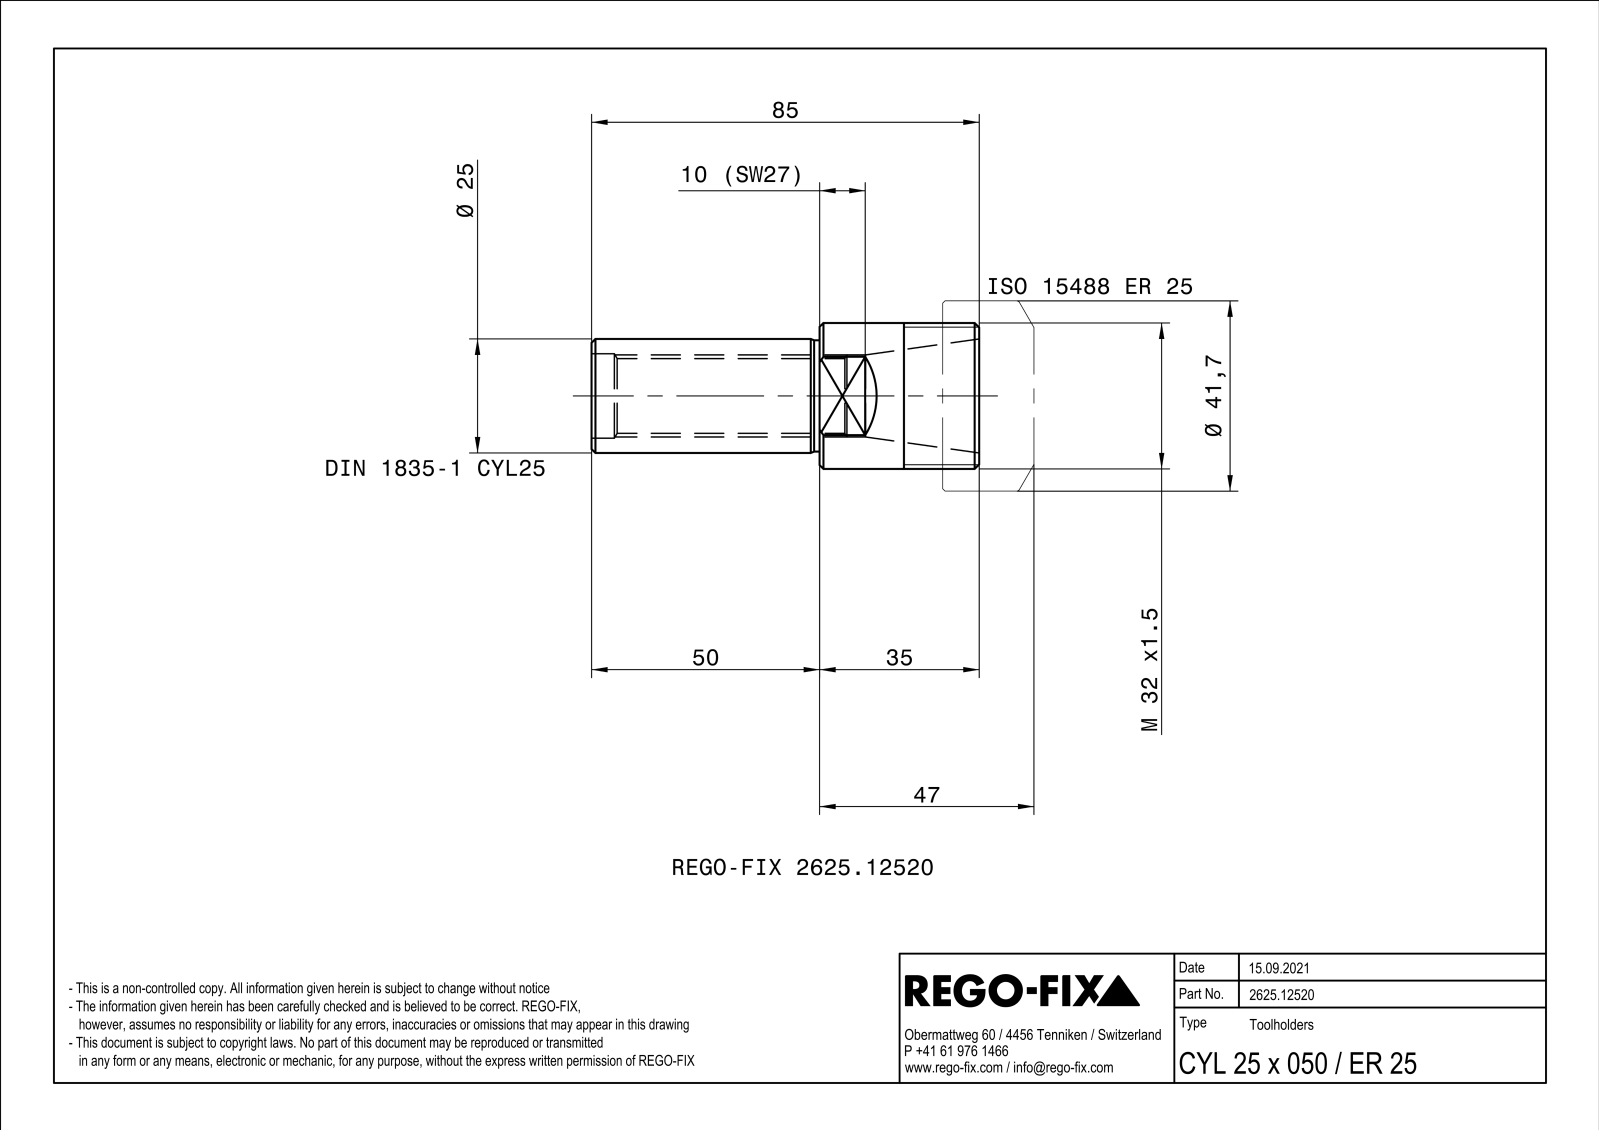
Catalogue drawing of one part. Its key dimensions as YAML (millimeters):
part_name: "NOCUT"
step_written_by: "SIEMENS PLM Software Solid Edge ST10 (AUTOMOTIVE_DESIGN)"
units: millimeters
bodies: {solids: 1, faces: 32, planar: 12, cylindrical: 7, other: 13}
overall_size: [85, 32, 32]
volume: 29633
surface_area: 12948
round_holes:
  - {diameter: 16.38, count: 1}
  - {diameter: 18, count: 1}
  - {diameter: 18.5, count: 1}
round_bosses_or_shafts:
  - {diameter: 32, count: 1}
  - {diameter: 25, count: 1}
  - {diameter: 24.6, count: 1}
face_to_face_distances: [27, 35, 85, 50, 6.47]
